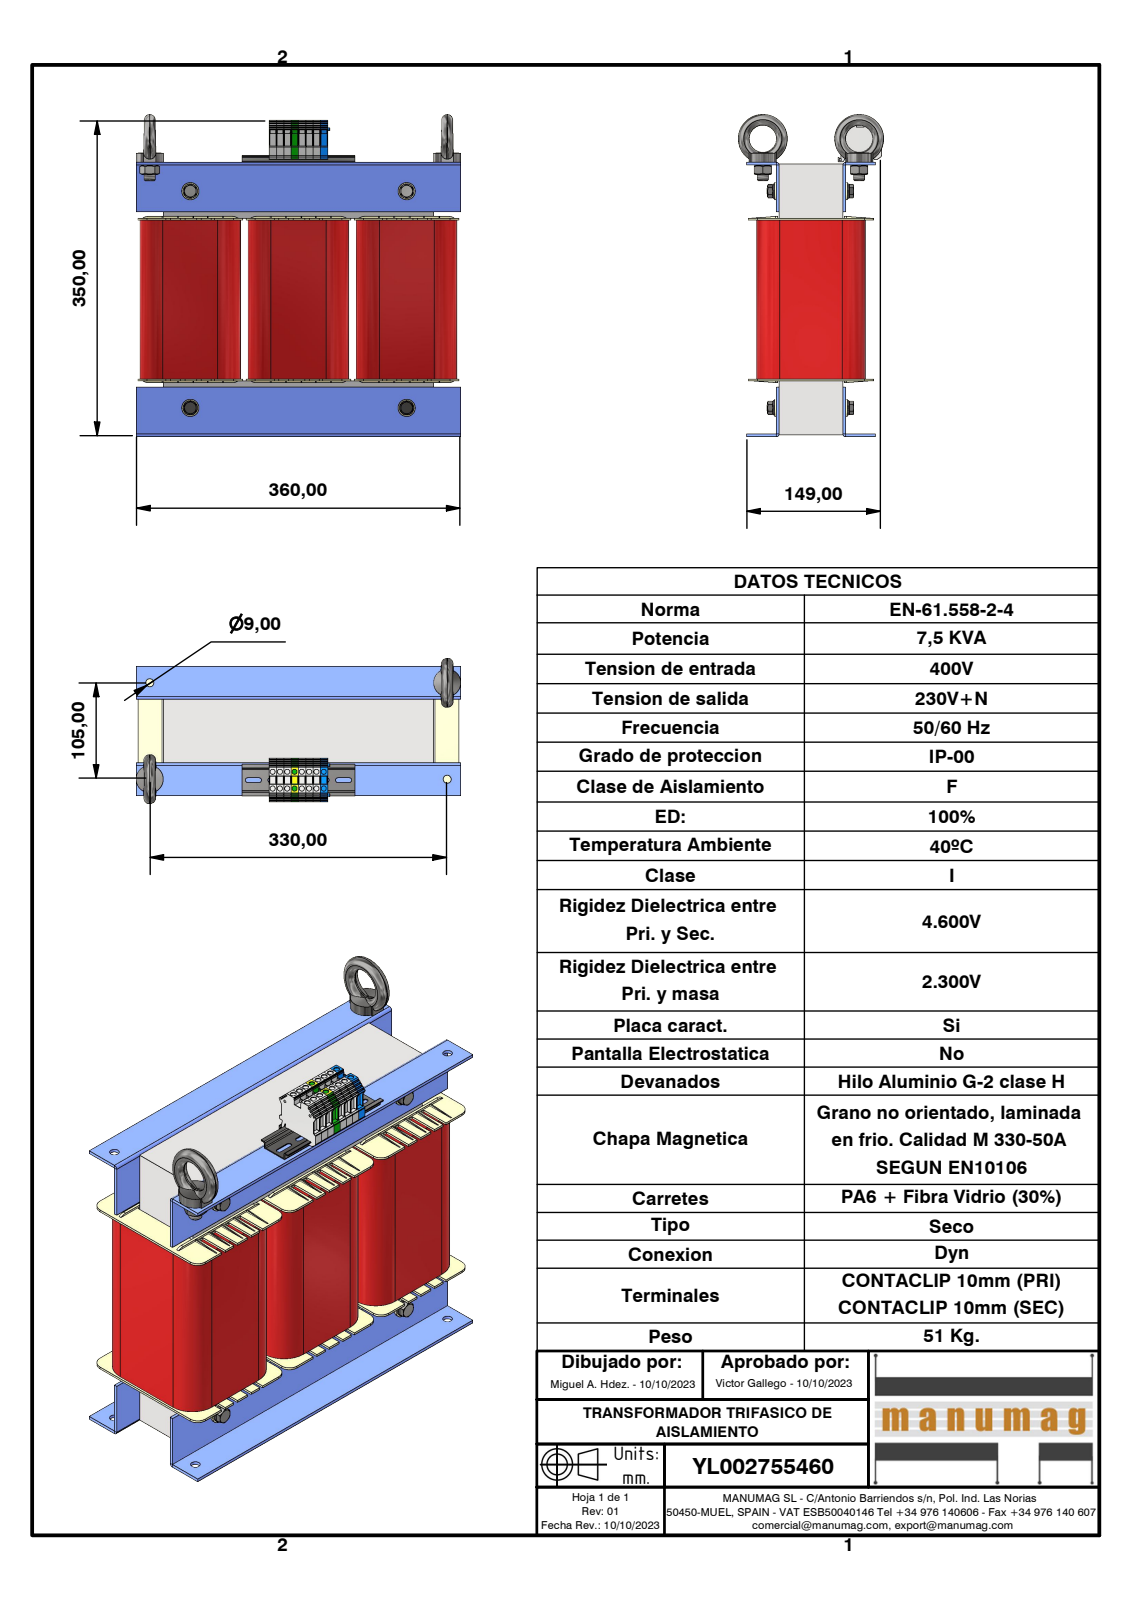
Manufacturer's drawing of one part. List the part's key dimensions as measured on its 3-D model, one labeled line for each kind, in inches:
Part name (STEP PRODUCT): YL002755460; UI 180 - 70 (300x300); UI 180_70_BOBINADO; RC60 NT060 (+8 more)
STEP written by: Autodesk Inventor 2023 (AUTOMOTIVE_DESIGN)
Units: inches
Bodies: 45 solids, 3384 faces (2398 planar, 798 cylindrical, 188 other)
Overall size (bounding box): 14.173 × 14.055 × 6.299
Volume: 590.3 in³ · Surface area: 2 220 in²
Round holes (diameter × count): ⌀0.224 ×16, ⌀0.262 ×4, ⌀0.315 ×4, ⌀0.331 ×4, ⌀0.354 ×4, ⌀0.413 ×4, ⌀0.433 ×4, ⌀0.094 ×2, ⌀0.098 ×2, ⌀0.108 ×2, ⌀0.398 ×2, ⌀1.181 ×2
Round bosses / shafts (diameter × count): ⌀0.748 ×4, ⌀0.63 ×4, ⌀0.449 ×4, ⌀0.378 ×4, ⌀0.288 ×4, ⌀2.126 ×2, ⌀0.472 ×2, ⌀0.425 ×2
Partial cylindrical surfaces — rounded edges, fillets, slot ends (radius × count): R0.012 ×81, R0.039 ×28, R0.394 ×24, R0.079 ×17, R0.118 ×12, R0.13 ×12, R0.999 ×12, R0.102 ×10
Main face-to-face distances: 0.098, 0.039, 9.449, 0.059, 0.118, 2.874, 2.362, 2.756, 4.724, 0.869
Hole centre spacings: 0.319, 0.791, 0.638, 0.965, 0.957, 1.2, 0.724, 1.276
